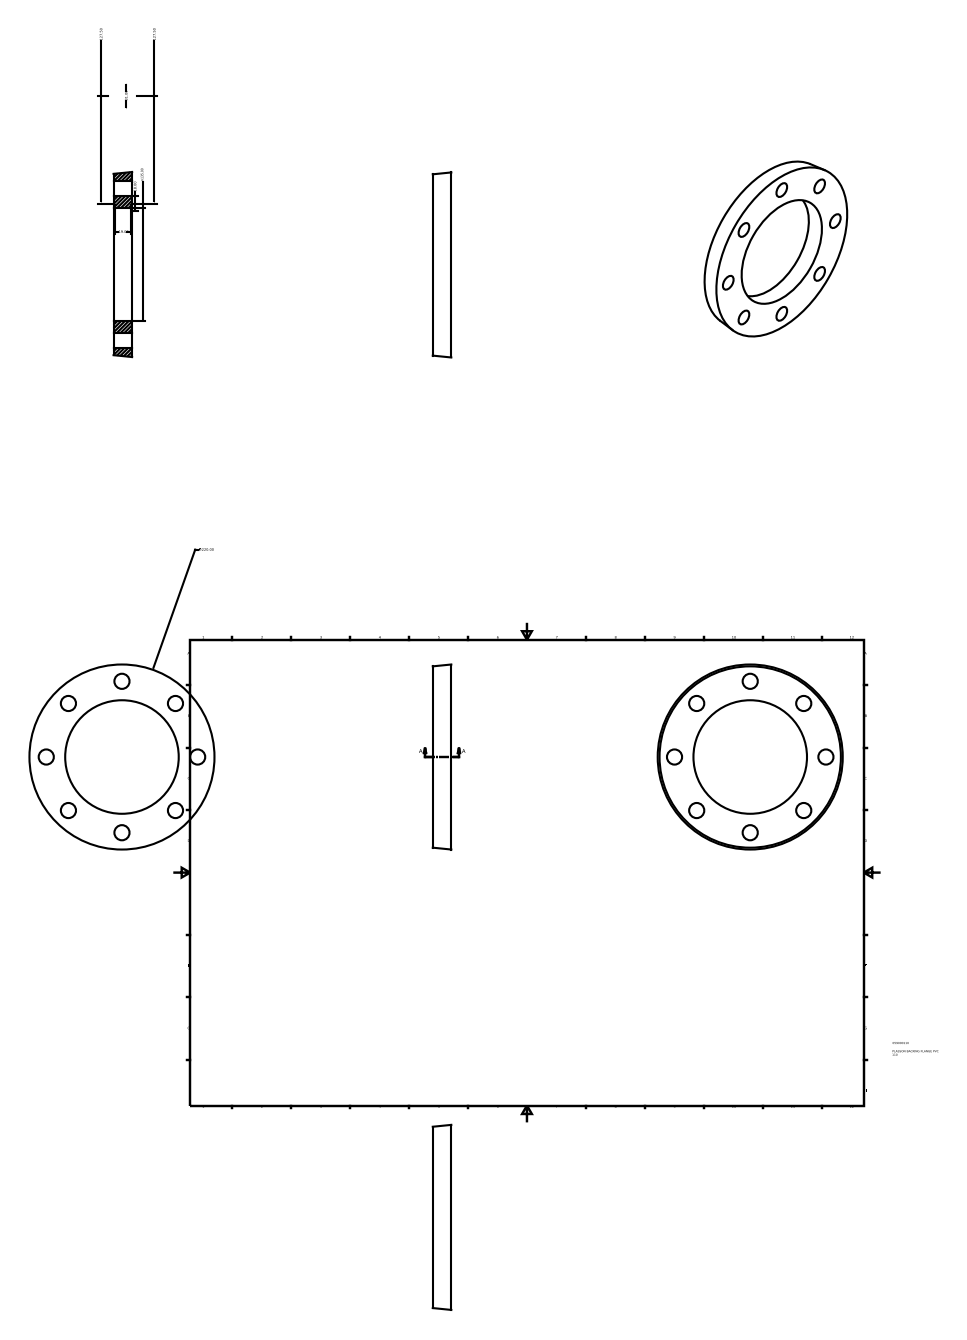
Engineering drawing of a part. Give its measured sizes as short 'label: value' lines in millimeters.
name: 059000110
written by: Autodesk Inventor 2015 (AUTOMOTIVE_DESIGN)
unit: mm
bodies: 1 solid, 12 faces (2 planar, 9 cylindrical, 1 other)
size: 220 × 220 × 22
volume: 459 986 mm³; area: 76 233 mm²
holes: 8× ⌀18, 1× ⌀135
face distances: 22
hole spacings: 68.88, 90, 127.28, 166.3, 180
